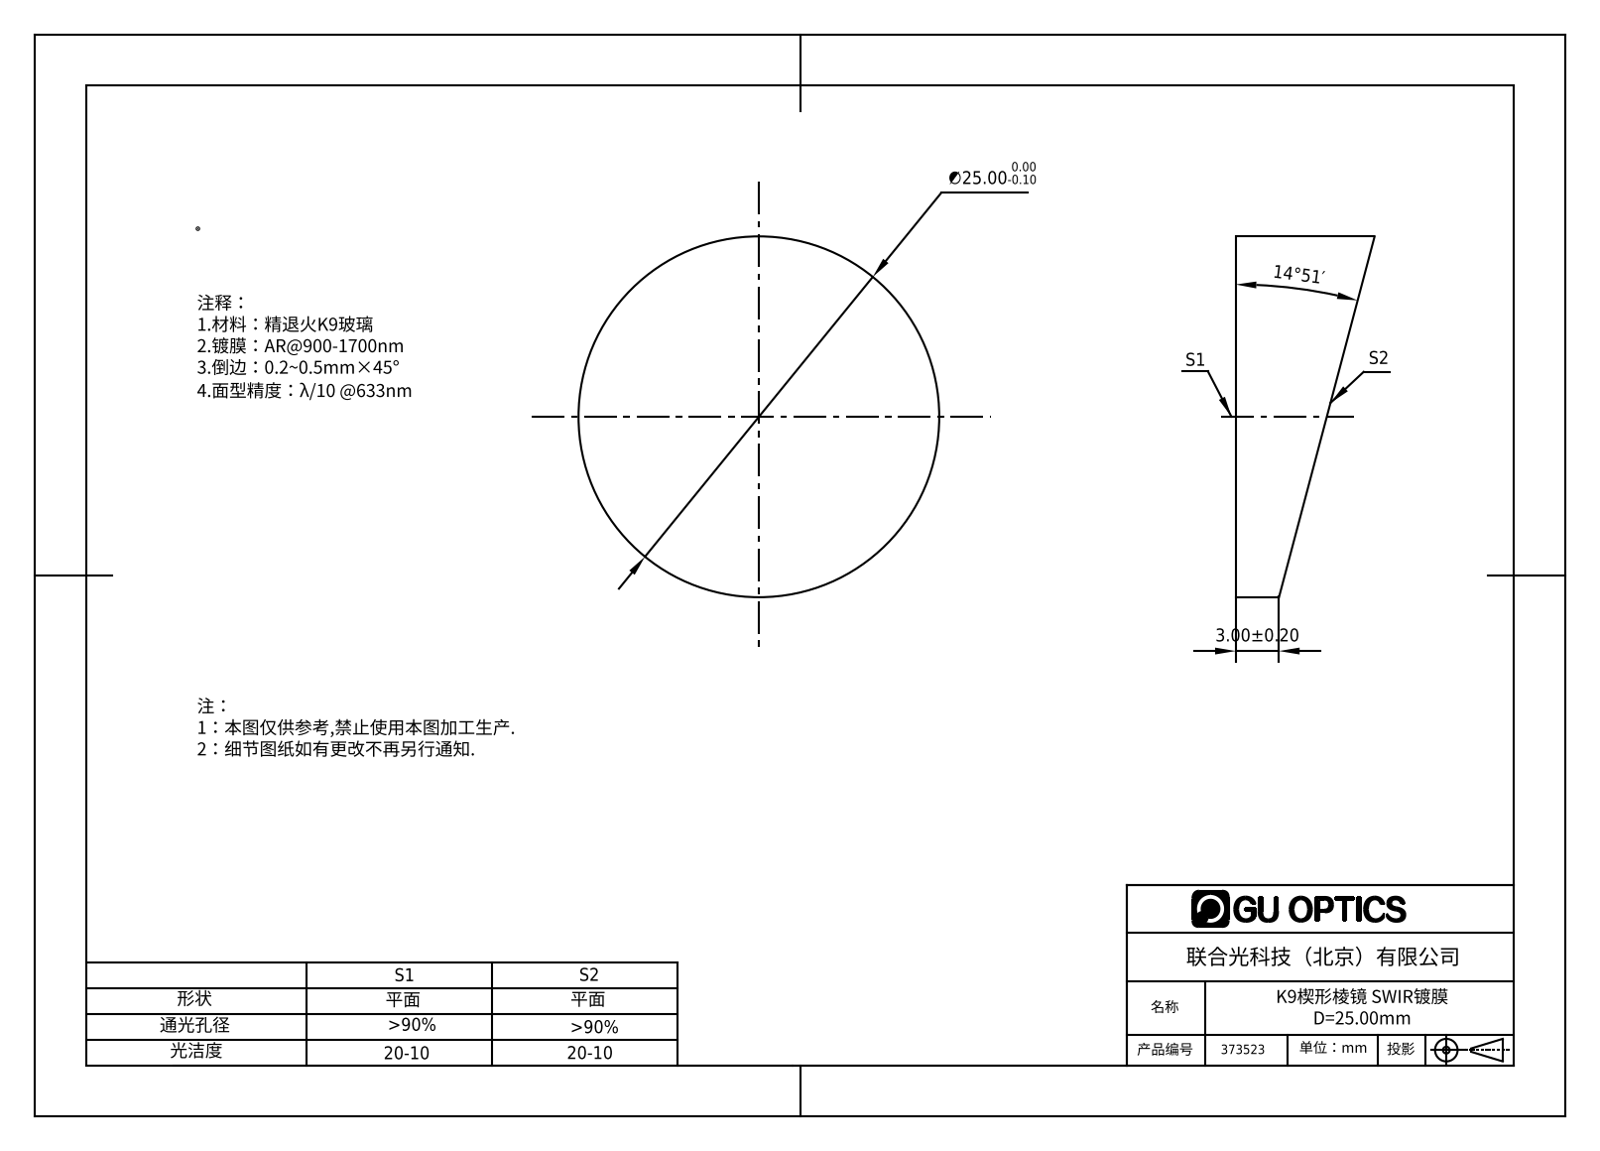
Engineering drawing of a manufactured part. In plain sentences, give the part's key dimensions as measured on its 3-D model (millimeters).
The part is named "373520". Its 3-D file was written by "SolidWorks 2016 (CONFIG_CONTROL_DESIGN)". It is 1 solid with 4 faces: 2 planar, 2 cylindrical and 0 other. Overall it measures 25 by 25 by 9.63 millimeters. Its volume is 3 100 cubic millimeters and its surface area 1 495 square millimeters. Round bosses or shafts: 1 of diameter 25.
